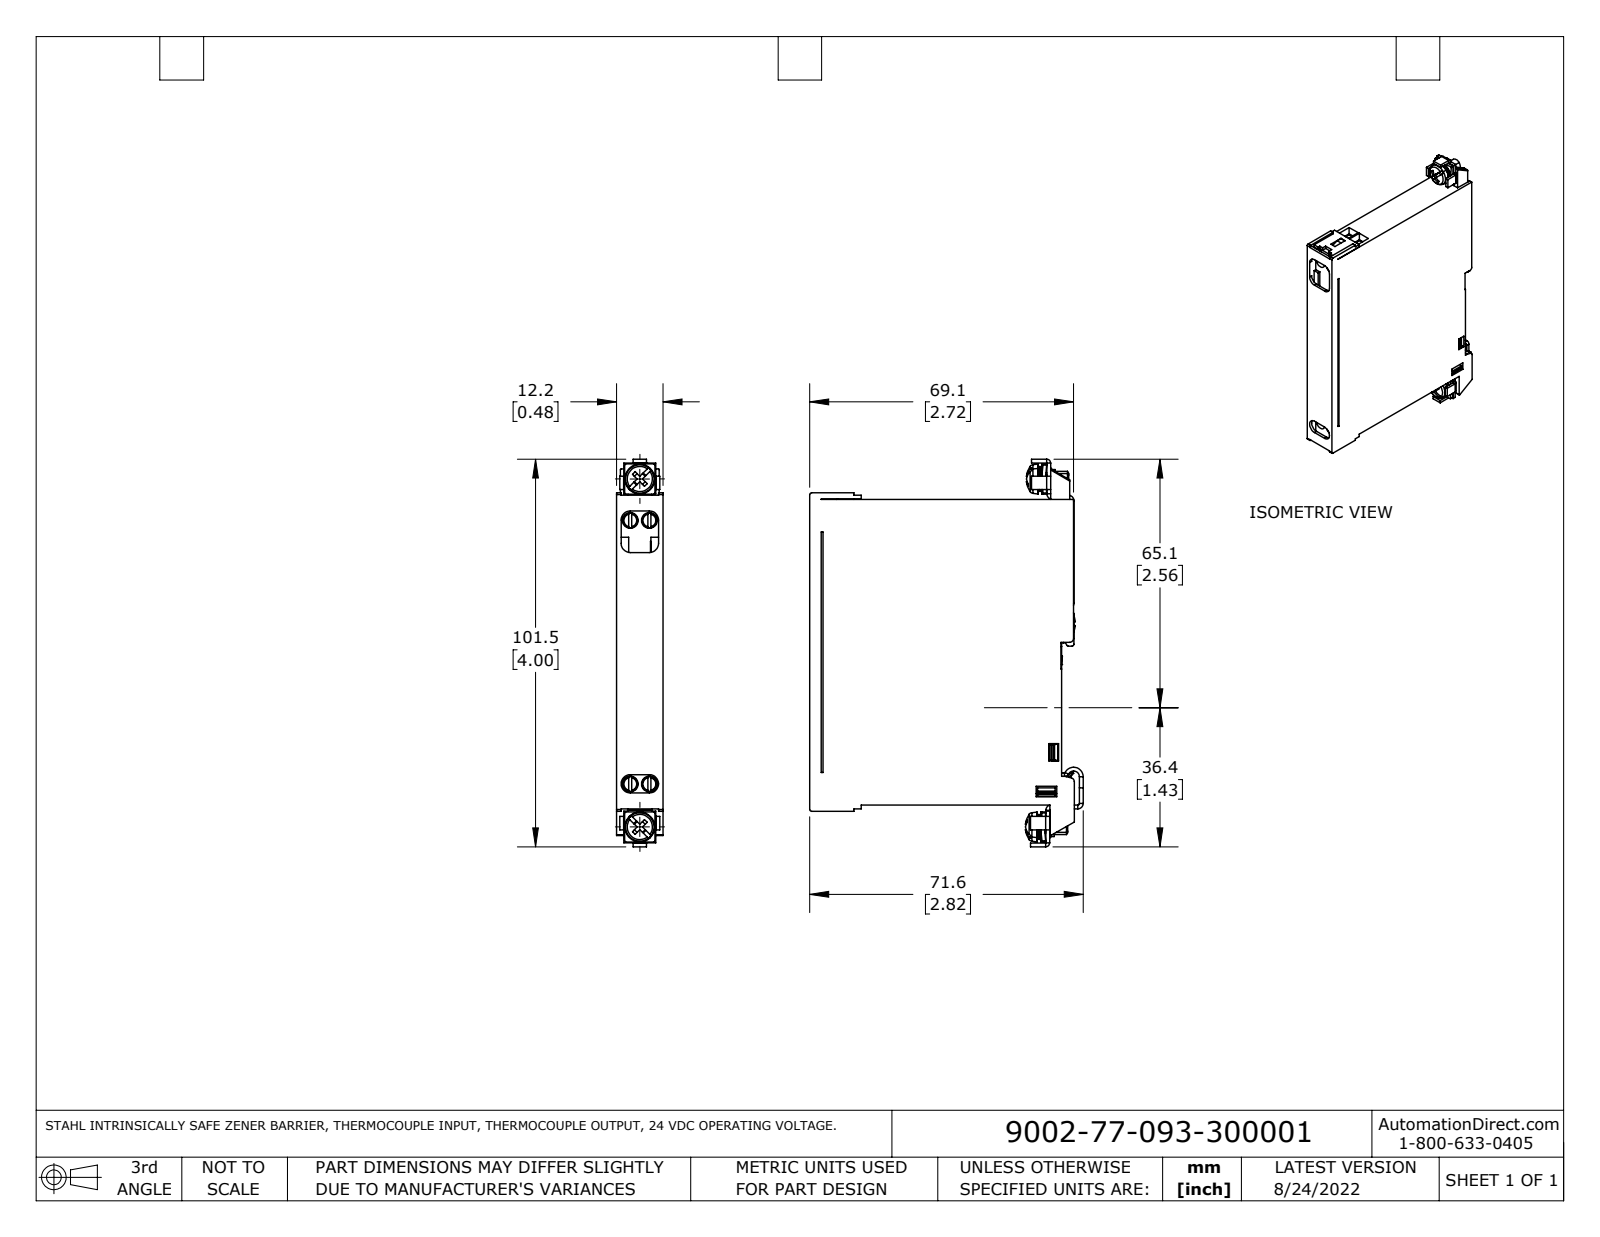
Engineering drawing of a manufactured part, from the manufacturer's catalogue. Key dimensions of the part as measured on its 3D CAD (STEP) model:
Part name (STEP PRODUCT): 9002-77-093-300001
STEP written by: SolidWorks 2021 (AUTOMOTIVE_DESIGN)
Units: inches
Bodies: 5 solids, 1525 faces (1084 planar, 281 cylindrical, 160 other)
Overall size (bounding box): 3.996 × 2.82 × 0.48
Volume: 1.34 in³ · Surface area: 56.34 in²
Round holes (diameter × count): ⌀0.051 ×5, ⌀0.063 ×5, ⌀0.161 ×4, ⌀0.016 ×2, ⌀0.128 ×2, ⌀0.165 ×2, ⌀0.067 ×1, ⌀0.118 ×1, ⌀0.169 ×1, ⌀0.228 ×1, ⌀0.26 ×1
Round bosses / shafts (diameter × count): ⌀0.047 ×6, ⌀0.307 ×3, ⌀0.157 ×3, ⌀0.197 ×2, ⌀0.124 ×2, ⌀0.315 ×1, ⌀0.256 ×1
Partial cylindrical surfaces — rounded edges, fillets, slot ends (radius × count): R0.02 ×36, R0.012 ×12, R0.008 ×11, R0.039 ×8, R0.016 ×6, R0.032 ×6, R0.041 ×6, R0.055 ×6
Main face-to-face distances: 0.039, 0.441, 0.48, 0.402, 0.043, 0.079, 0.083, 2.559, 0.118, 3.11
Hole centre spacings: 0.15, 0.462, 0.197, 0.28, 0.293, 0.299, 0.371, 0.421
